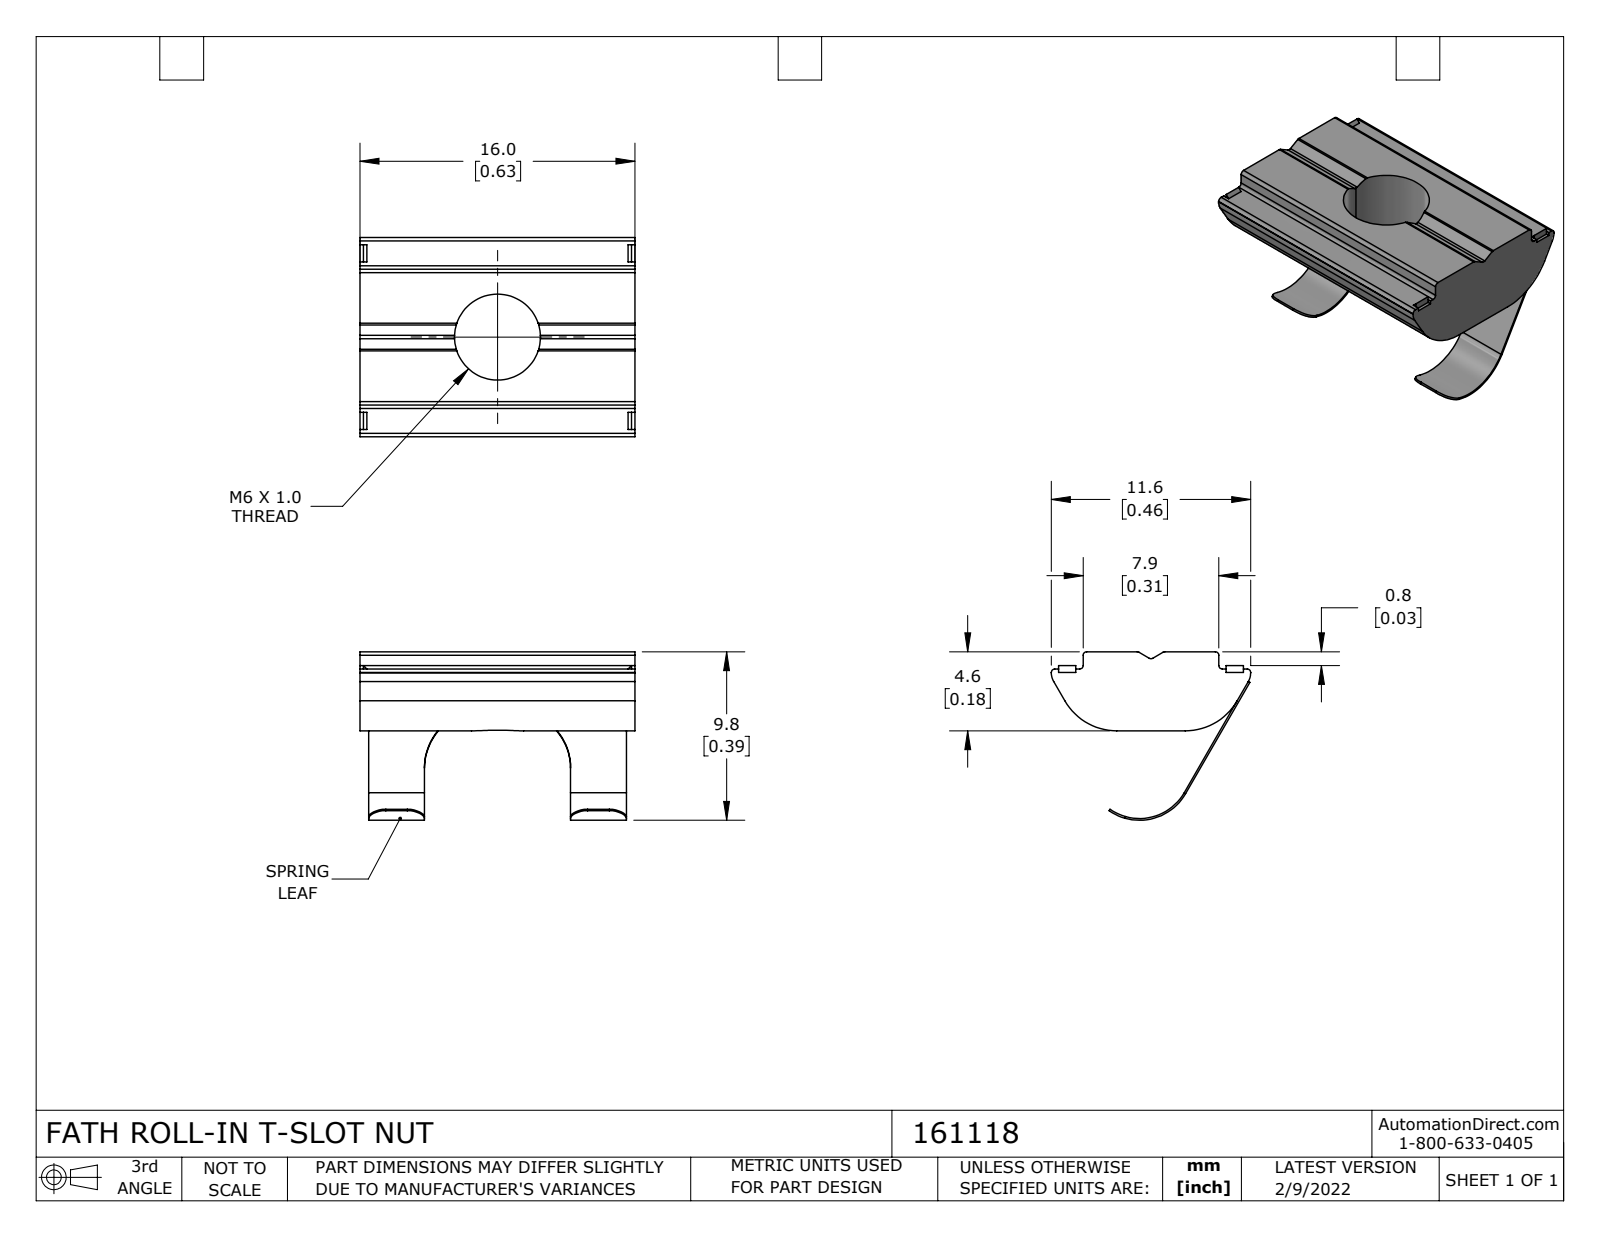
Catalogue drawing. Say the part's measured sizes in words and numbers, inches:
The part is named "161118". Its 3-D file was written by "SolidWorks 2021 (CONFIG_CONTROL_DESIGN)". It is 1 solid with 84 faces: 56 planar, 28 cylindrical and 0 other. Overall it measures 0.63 by 0.457 by 0.386 inches. Its volume is 0.037 cubic inches and its surface area 1.16 square inches. Round holes: 1 of diameter 0.197. Partial cylindrical surfaces (rounded edges, fillets, slot ends): 9 of radius 0.008, 6 of radius 0.039, 2 of radius 0.138, 1 of radius 0.118, 1 of radius 0.122, 1 of radius 0.167. The main face-to-face distances are 0.181, 0.039, 0.142, 0.63, 0.311, 0.02, 0.61, 0.622, 0.602, 0.067.
